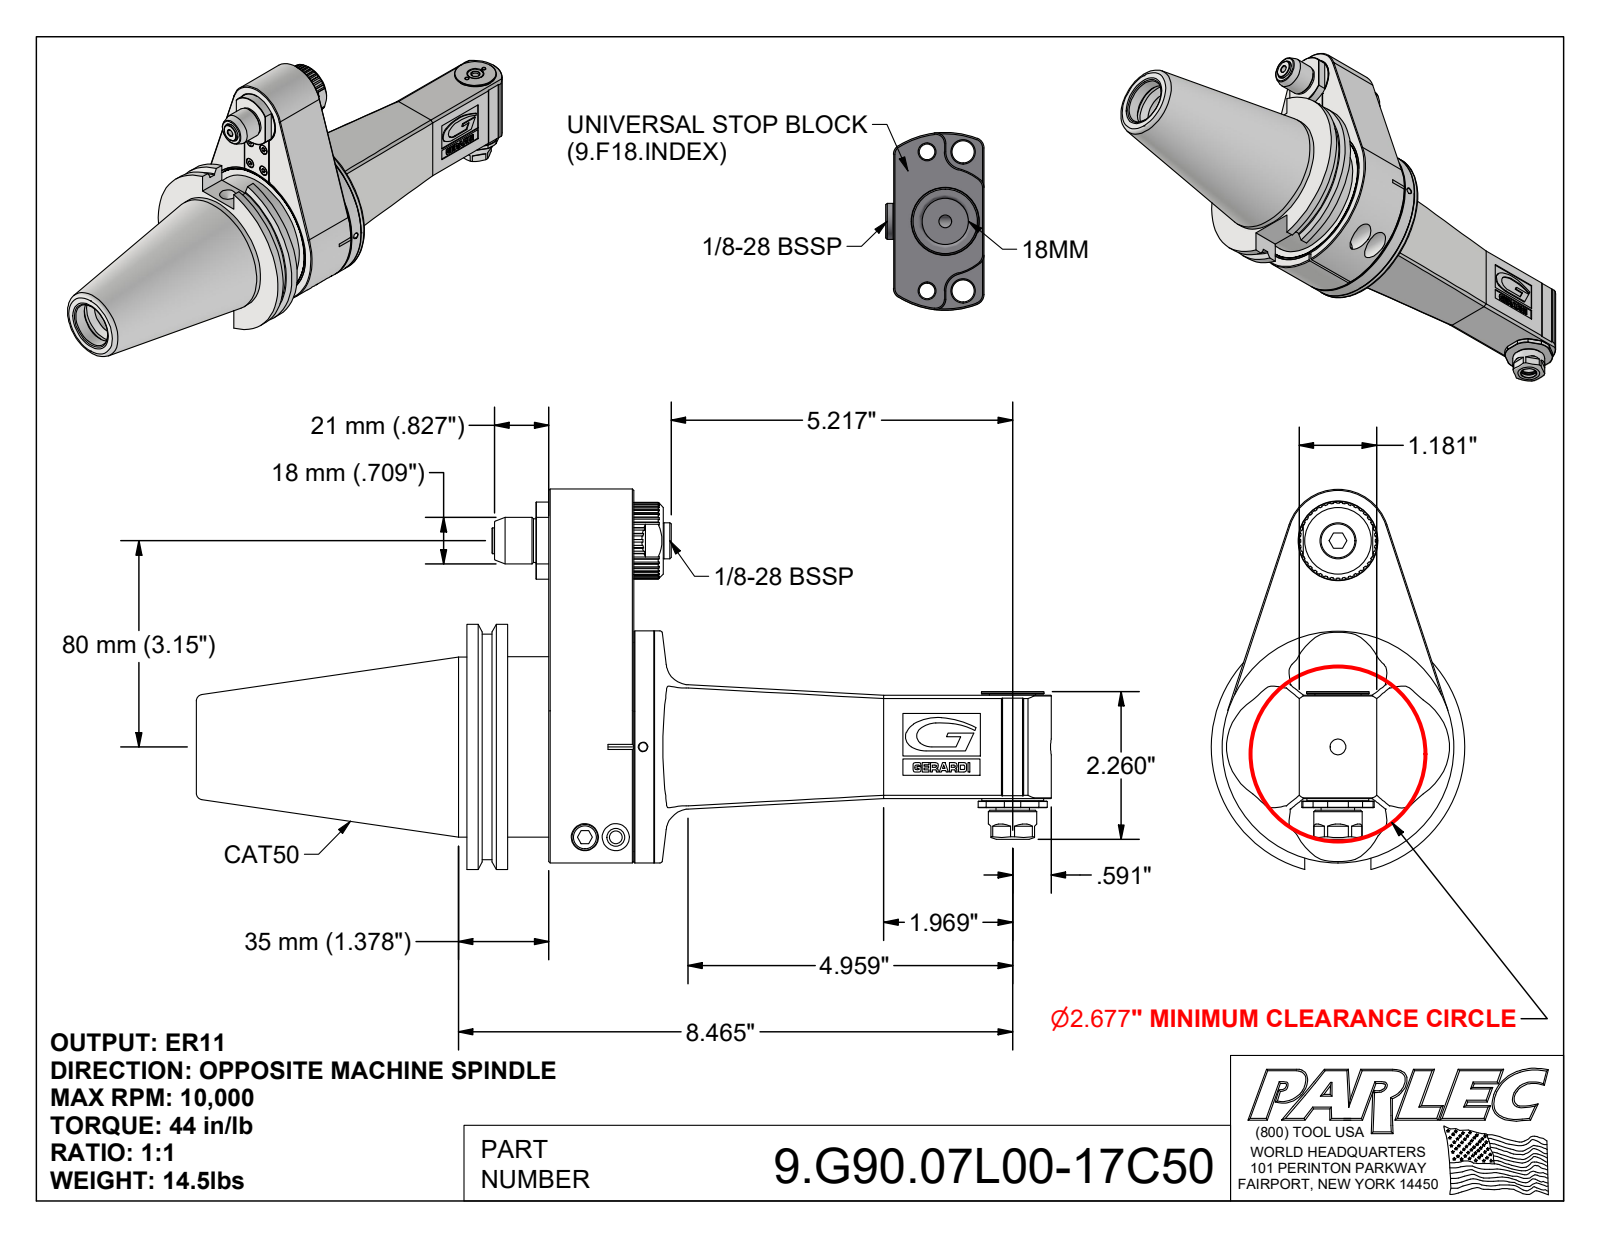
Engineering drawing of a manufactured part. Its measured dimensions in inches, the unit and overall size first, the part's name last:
Units: inches
Overall size (bounding box): 13.063 × 5.807 × 3.875
Round holes (diameter × count): ⌀0.165 ×6, ⌀0.197 ×4, ⌀0.236 ×4, ⌀0.083 ×2, ⌀0.157 ×2, ⌀0.276 ×2, ⌀0.335 ×2, ⌀0.413 ×2, ⌀0.13 ×1, ⌀0.24 ×1, ⌀0.354 ×1, ⌀0.433 ×1
Round bosses / shafts (diameter × count): ⌀0.394 ×3, ⌀3.875 ×1, ⌀3.593 ×1, ⌀3.543 ×1, ⌀3.071 ×1, ⌀2.75 ×1, ⌀1 ×1, ⌀0.957 ×1
Partial cylindrical surfaces — rounded edges, fillets, slot ends (radius × count): R0.354 ×4, R0.085 ×2, R0.079 ×1, R0.098 ×1, R0.138 ×1, R0.181 ×1, R0.249 ×1, R0.295 ×1
Main face-to-face distances: 1.299, 0.626, 0.315, 0.984, 1.173, 1.252, 1.925, 0.941, 1.567, 2.551
Hole centre spacings: 1.476, 2.557, 0.764, 1.476, 2.088, 2.953, 0.276, 0.366
Volume: 59.38 in³ · Surface area: 231.9 in²
Bodies: 4 solids, 777 faces (435 planar, 158 cylindrical, 184 other)
Part name (STEP PRODUCT): 9.G90.07L00-17C50; 9_G90_07L00; 9_GA1_458_1 (Classic, Type 1, Cat50, 80mm)
STEP written by: Autodesk Inventor 2022 (AUTOMOTIVE_DESIGN)
